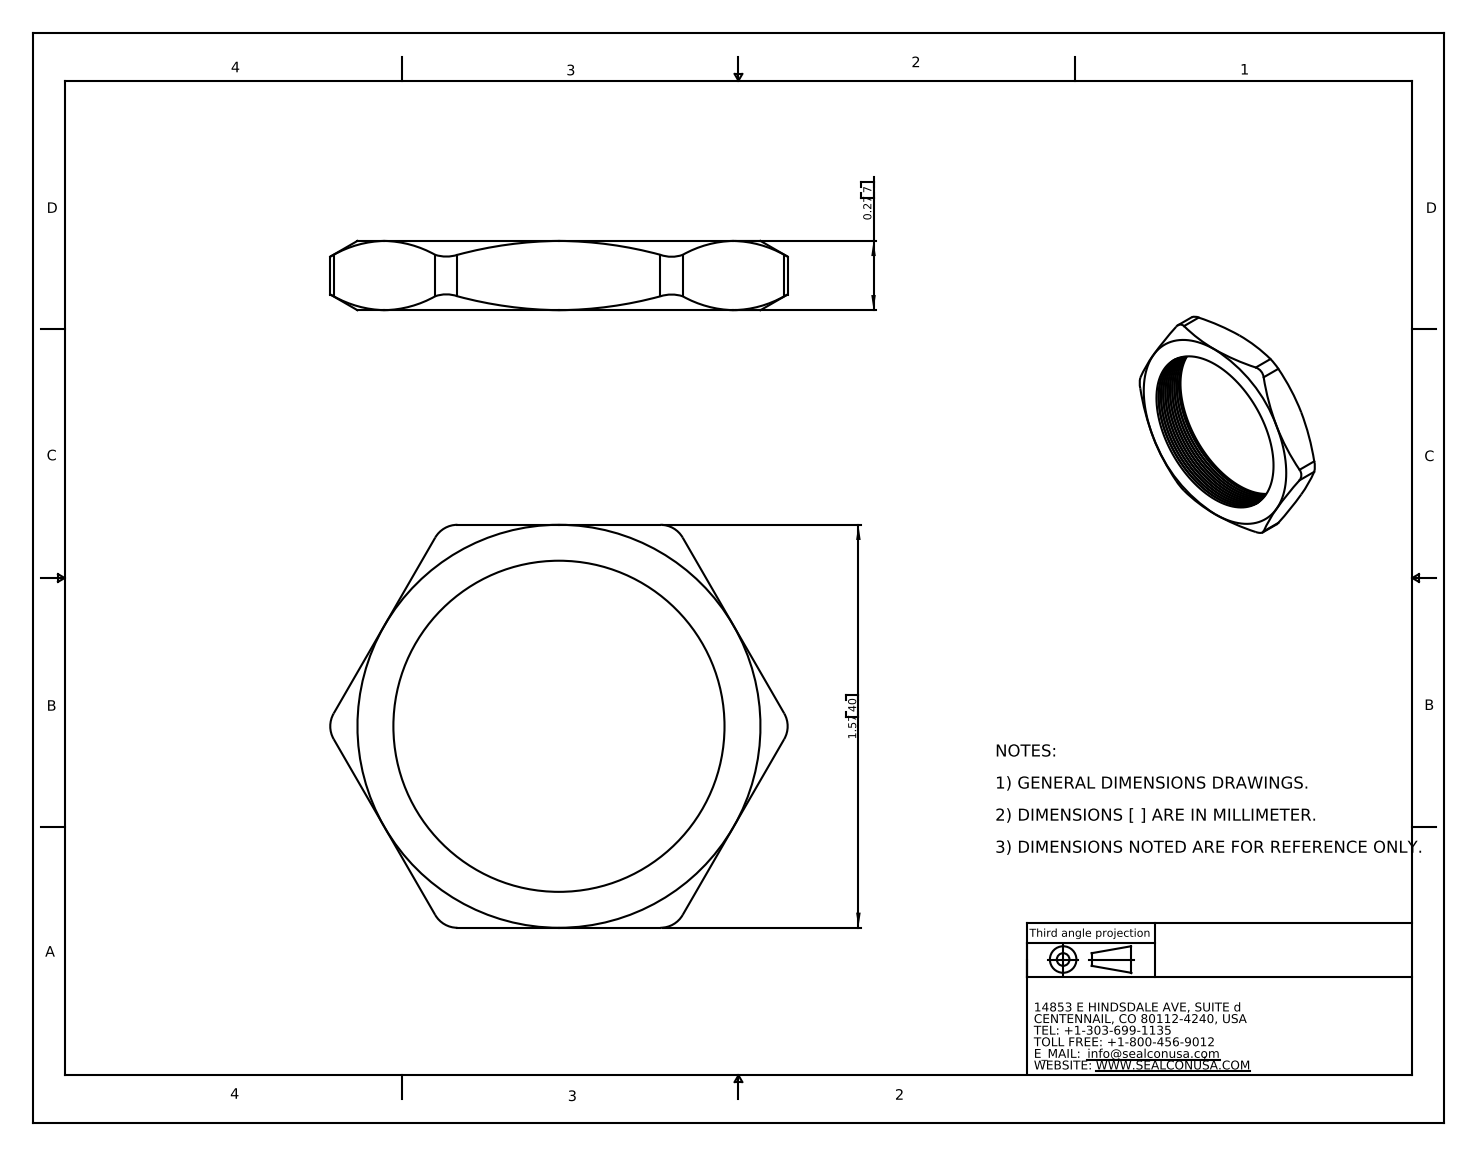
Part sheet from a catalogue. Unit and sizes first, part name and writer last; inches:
Units: inches
Overall size (bounding box): 1.782 × 1.57 × 0.27
Round holes (diameter × count): ⌀1.29 ×1
Partial cylindrical surfaces — rounded edges, fillets, slot ends (radius × count): R0.1 ×6
Main face-to-face distances: 0.27, 1.57
Volume: 0.204 in³ · Surface area: 5.032 in²
Bodies: 1 solid, 93 faces (8 planar, 27 cylindrical, 58 other)
Part name (STEP PRODUCT): NN-29
STEP written by: SolidWorks 2007 (CONFIG_CONTROL_DESIGN)
